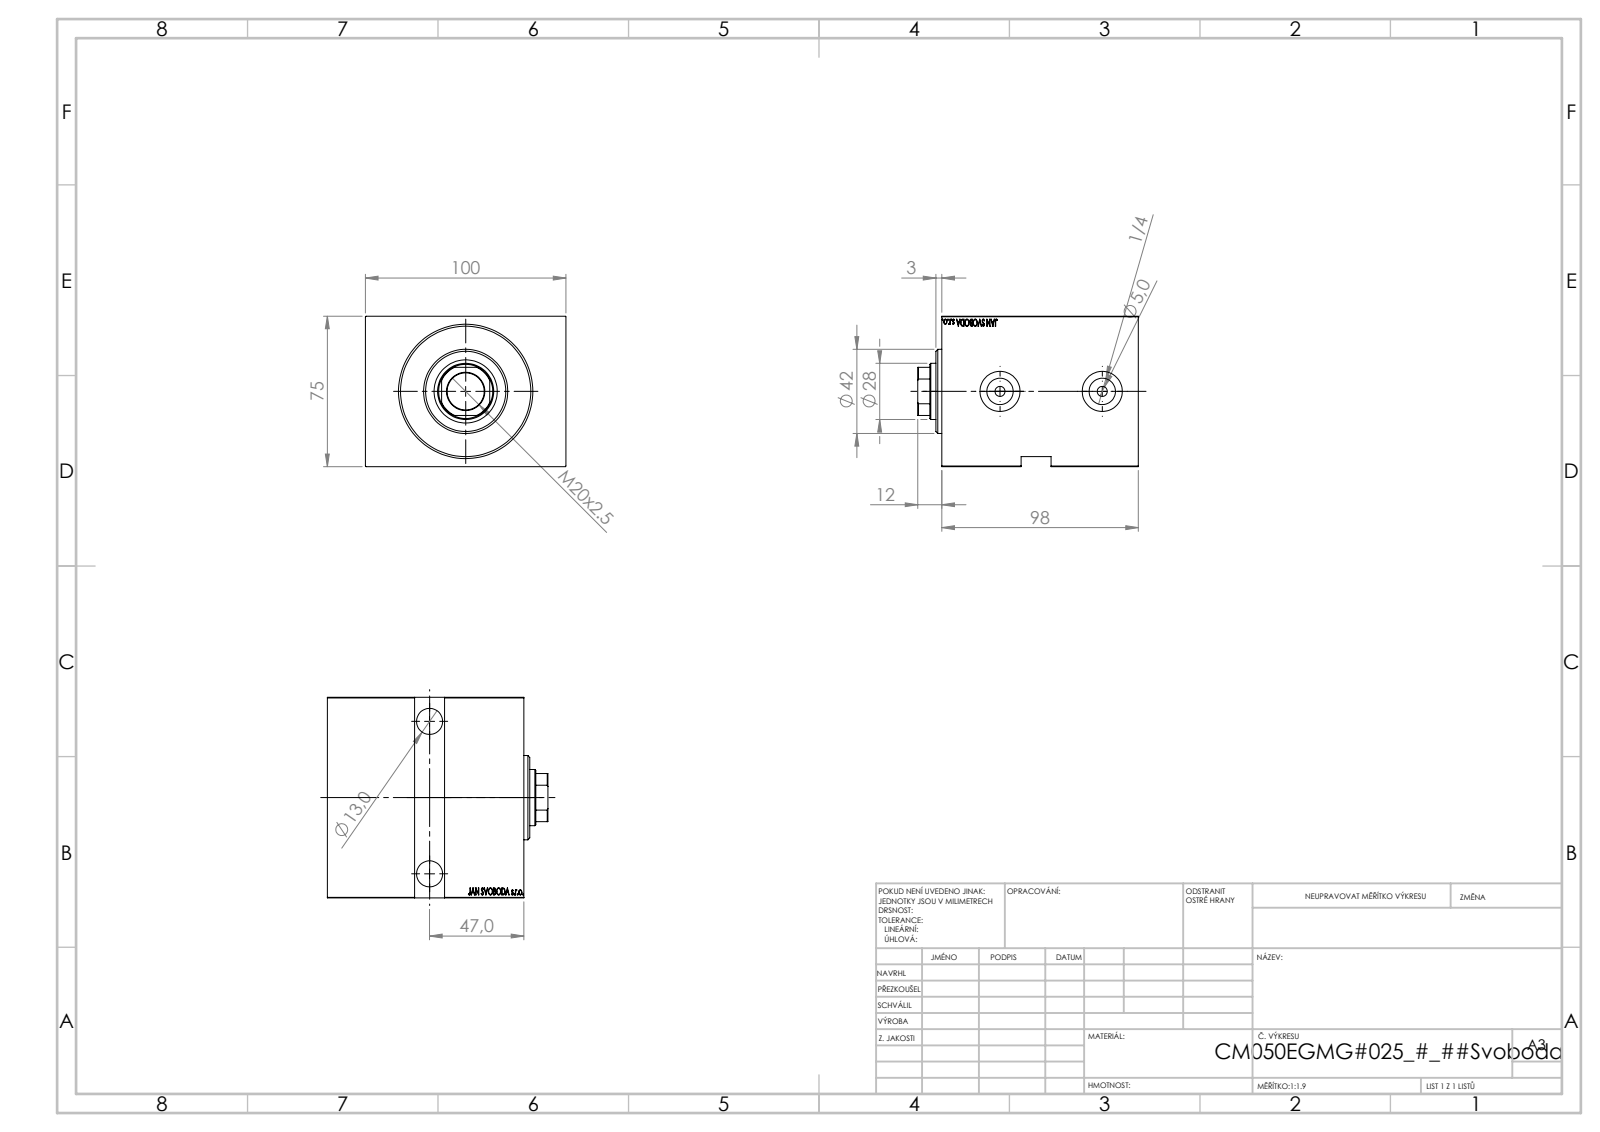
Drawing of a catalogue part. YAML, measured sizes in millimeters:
part_name: "V450CM_E_Body; V450CM_VC_B; V450CM_E_VCP"
step_written_by: "SolidWorks 2019 (CONFIG_CONTROL_DESIGN)"
units: millimeters
bodies: {solids: 3, faces: 848, planar: 410, cylindrical: 44, other: 394}
overall_size: [110, 100, 75]
volume: 674224
surface_area: 98309
round_holes:
  - {diameter: 5, count: 2}
  - {diameter: 13, count: 2}
  - {diameter: 13.16, count: 2}
  - {diameter: 19, count: 2}
  - {diameter: 20, count: 2}
  - {diameter: 18.5, count: 1}
  - {diameter: 28, count: 1}
  - {diameter: 31.5, count: 1}
  - {diameter: 50, count: 1}
  - {diameter: 65, count: 1}
round_bosses_or_shafts:
  - {diameter: 52, count: 1}
  - {diameter: 42, count: 1}
partial_cylinders:
  - {radius: 13.5, count: 1}
face_to_face_distances: [75, 100, 98, 14, 84, 5, 93, 79, 81.4, 67.4]
hole_center_spacings: [51, 76]
